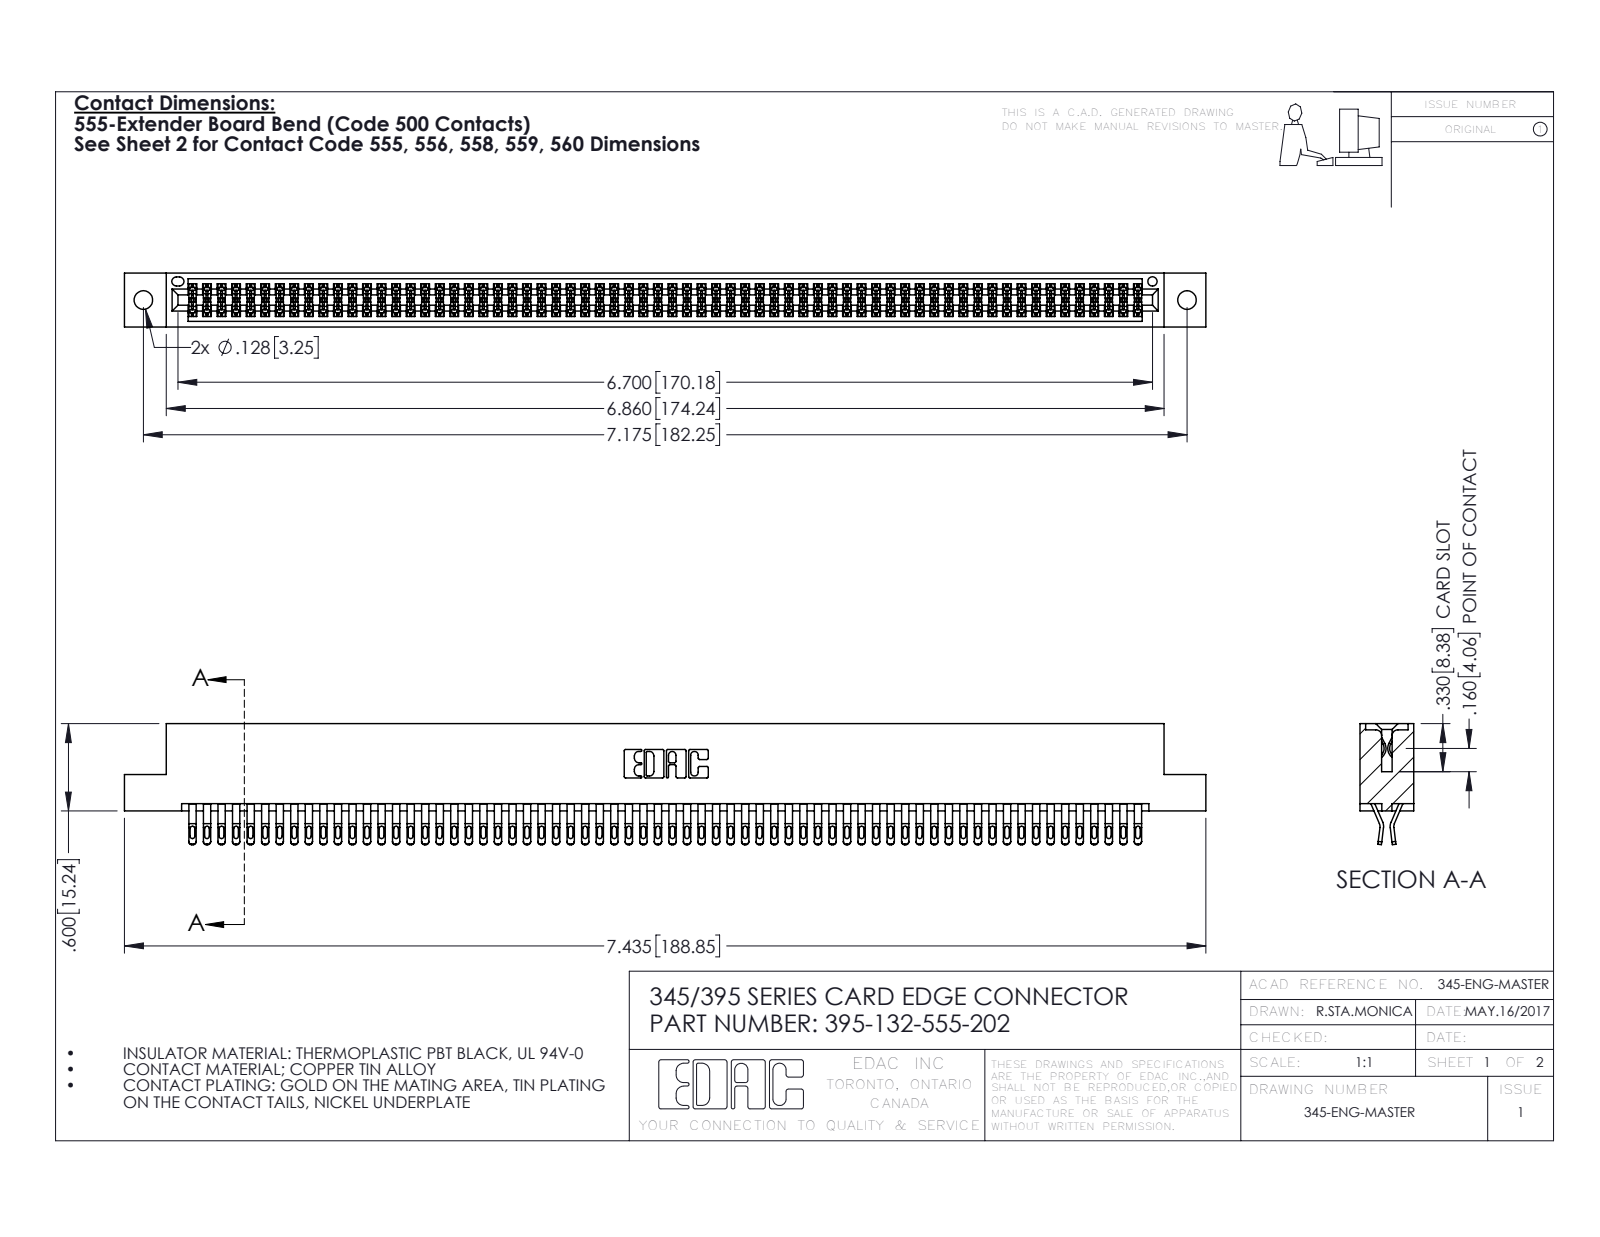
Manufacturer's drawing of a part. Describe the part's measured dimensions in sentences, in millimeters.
The part is named "345-292-001_555 Tail; 345 Part_Flush Mounting Lugs - 0.128 Dia; 395-132-555-202". Its 3-D file was written by "SolidWorks 2016 (CONFIG_CONTROL_DESIGN)". It is 133 solids with 7518 faces: 4172 planar, 3346 cylindrical and 0 other. Overall it measures 188.8 by 21.1 by 9.4 millimeters. Its volume is 18 910 cubic millimeters and its surface area 29 480 square millimeters. Round holes: 2 of diameter 3.3, 1 of diameter 1.6. Partial cylindrical surfaces (rounded edges, fillets, slot ends): 330 of radius 0.4, 264 of radius 0.5, 198 of radius 0.2, 22 of radius 0.3, 6 of radius 0.2, 6 of radius 0.8, 3 of radius 0.7, 2 of radius 0.3. The main face-to-face distances are 7.6, 1.8, 0.6, 9.4, 5.1, 2.5, 6.9, 5.7, 4.4, 3.8. The hole center spacings are 6.9, 176.3, 182.2.
